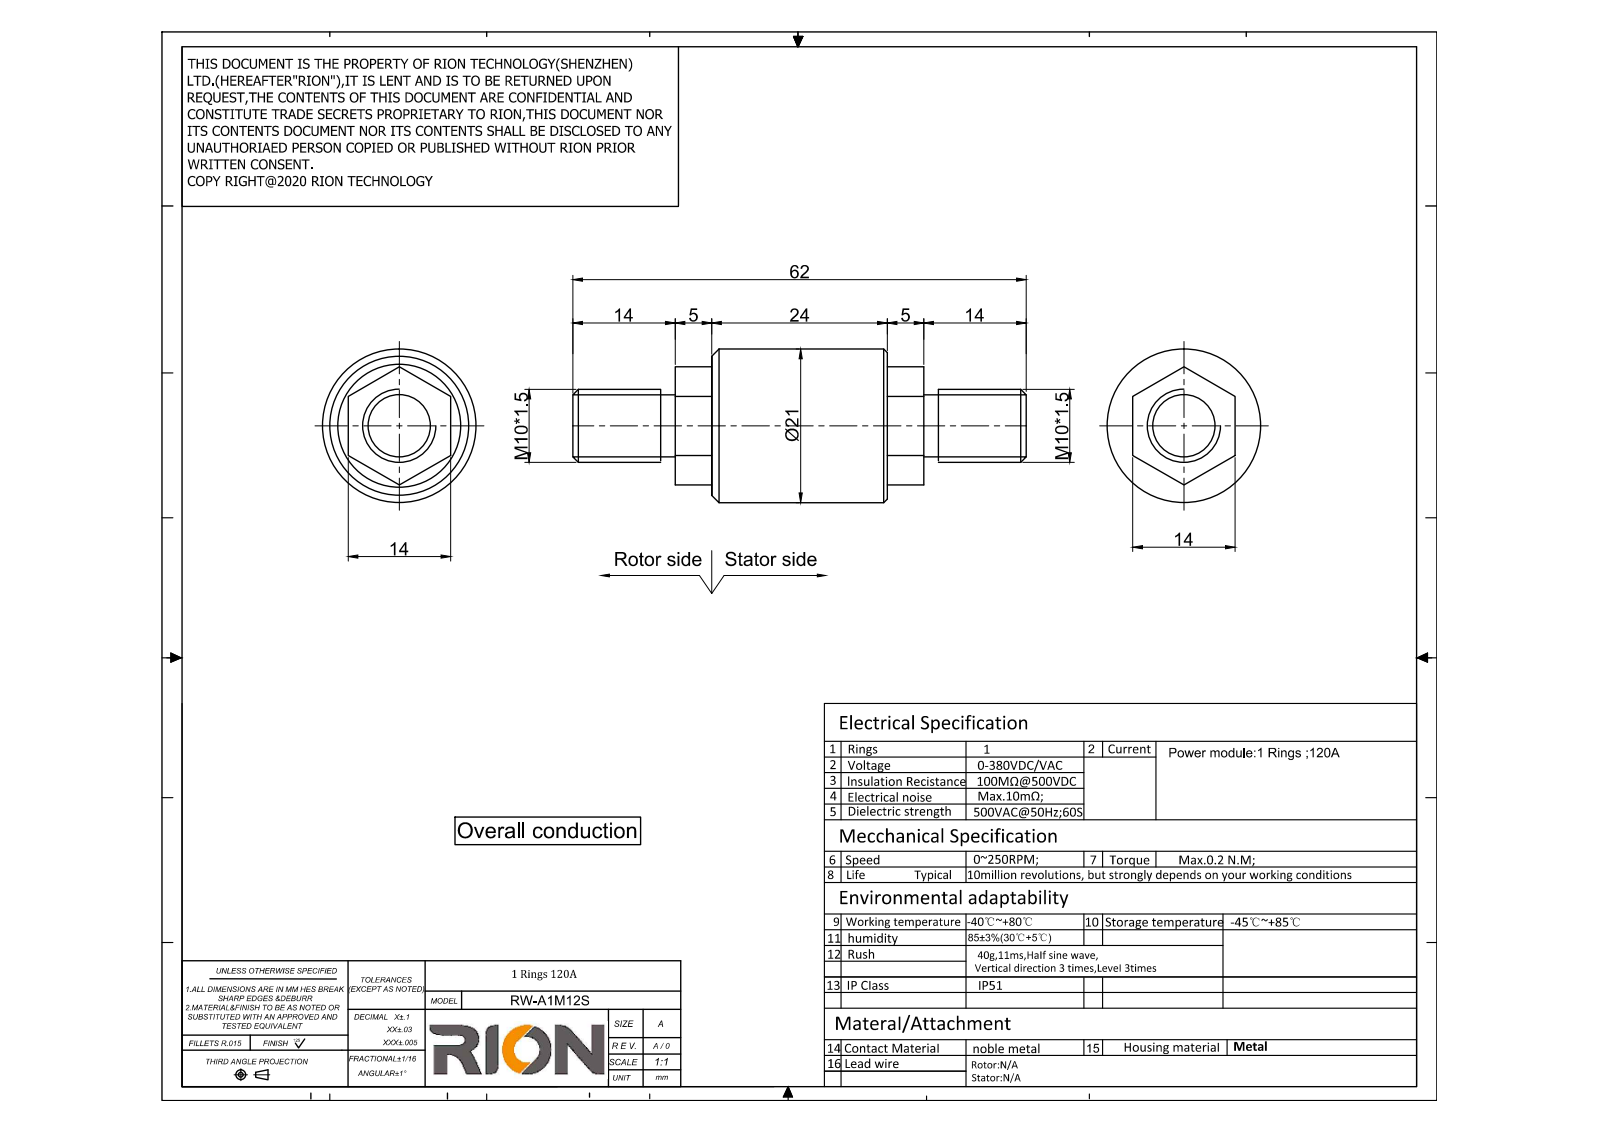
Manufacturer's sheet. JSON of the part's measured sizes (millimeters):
{"part_name": "Admi568CF6906h5z", "step_written_by": "SIEMENS PLM Software NX 8.5 (AUTOMOTIVE_DESIGN)", "units": "millimeters", "bodies": {"solids": 1, "faces": 31, "planar": 21, "cylindrical": 6, "other": 4}, "overall_size": [62, 21, 21], "volume_mm3": 12024, "surface_area_mm2": 3701, "round_holes": [[16.8, 1]], "round_bosses_or_shafts": [[21, 1], [10, 1], [8.5, 1]], "face_to_face_distances": [14, 29, 5, 19, 43, 48, 34, 24, 62, 19.8]}
